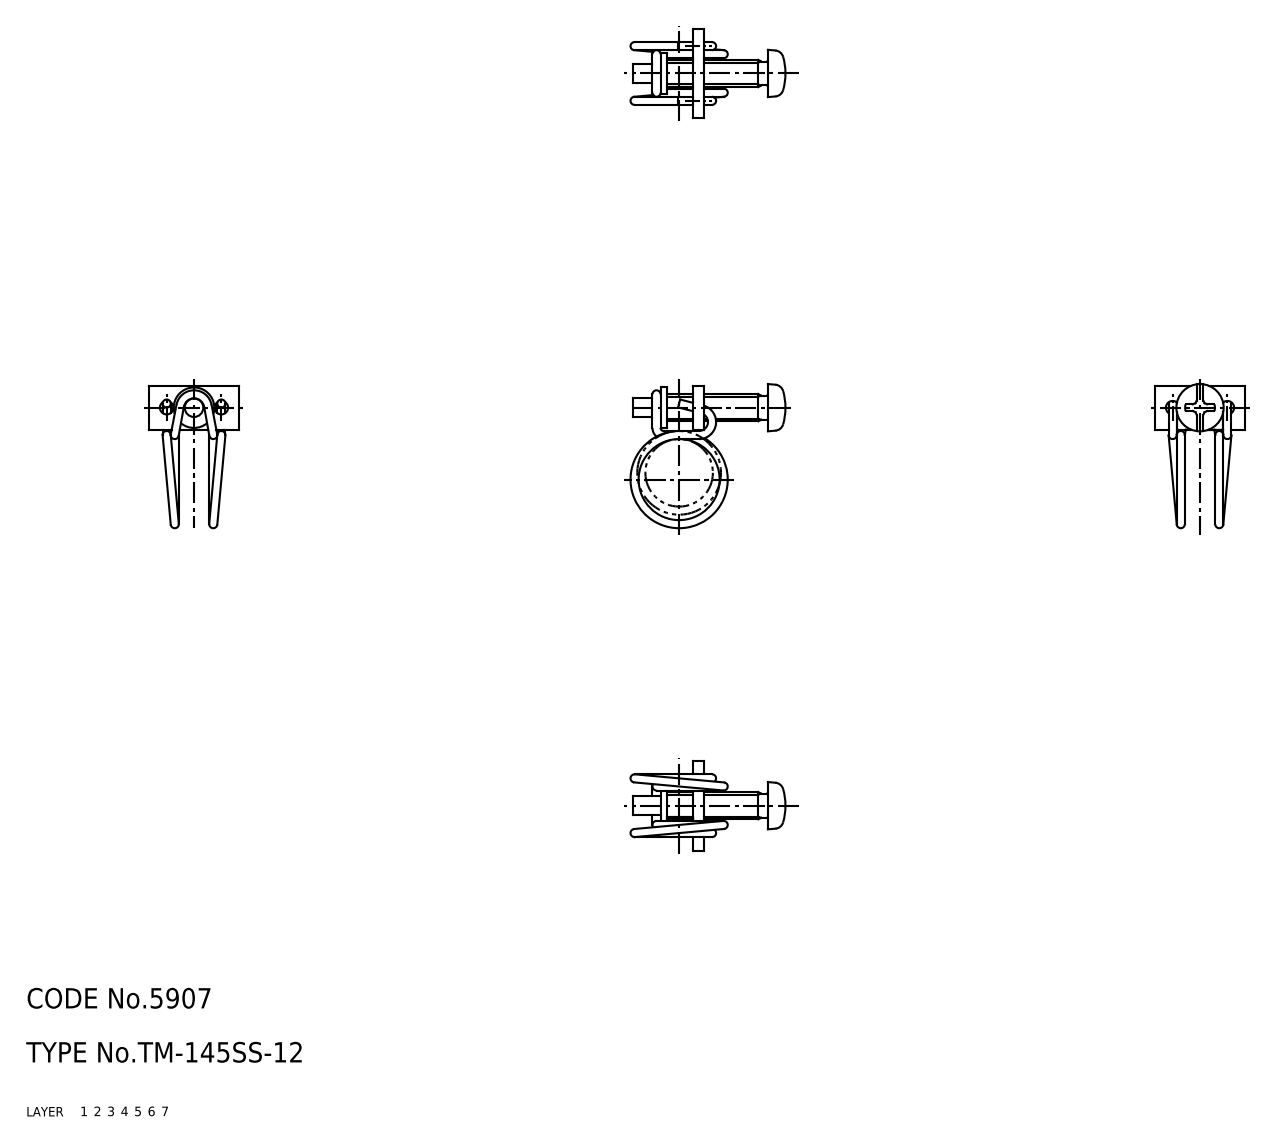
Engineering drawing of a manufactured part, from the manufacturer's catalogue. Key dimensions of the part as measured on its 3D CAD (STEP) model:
Part name (STEP PRODUCT): 67115499; 67115512; 67115525
STEP written by: CADfix (AUTOMOTIVE_DESIGN)
Units: millimetres
Bodies: 3 solids, 75 faces (0 planar, 0 cylindrical, 75 other)
Overall size (bounding box): 22.92 × 21.35 × 13.3
Volume: 562 mm³ · Surface area: 1 130 mm²
